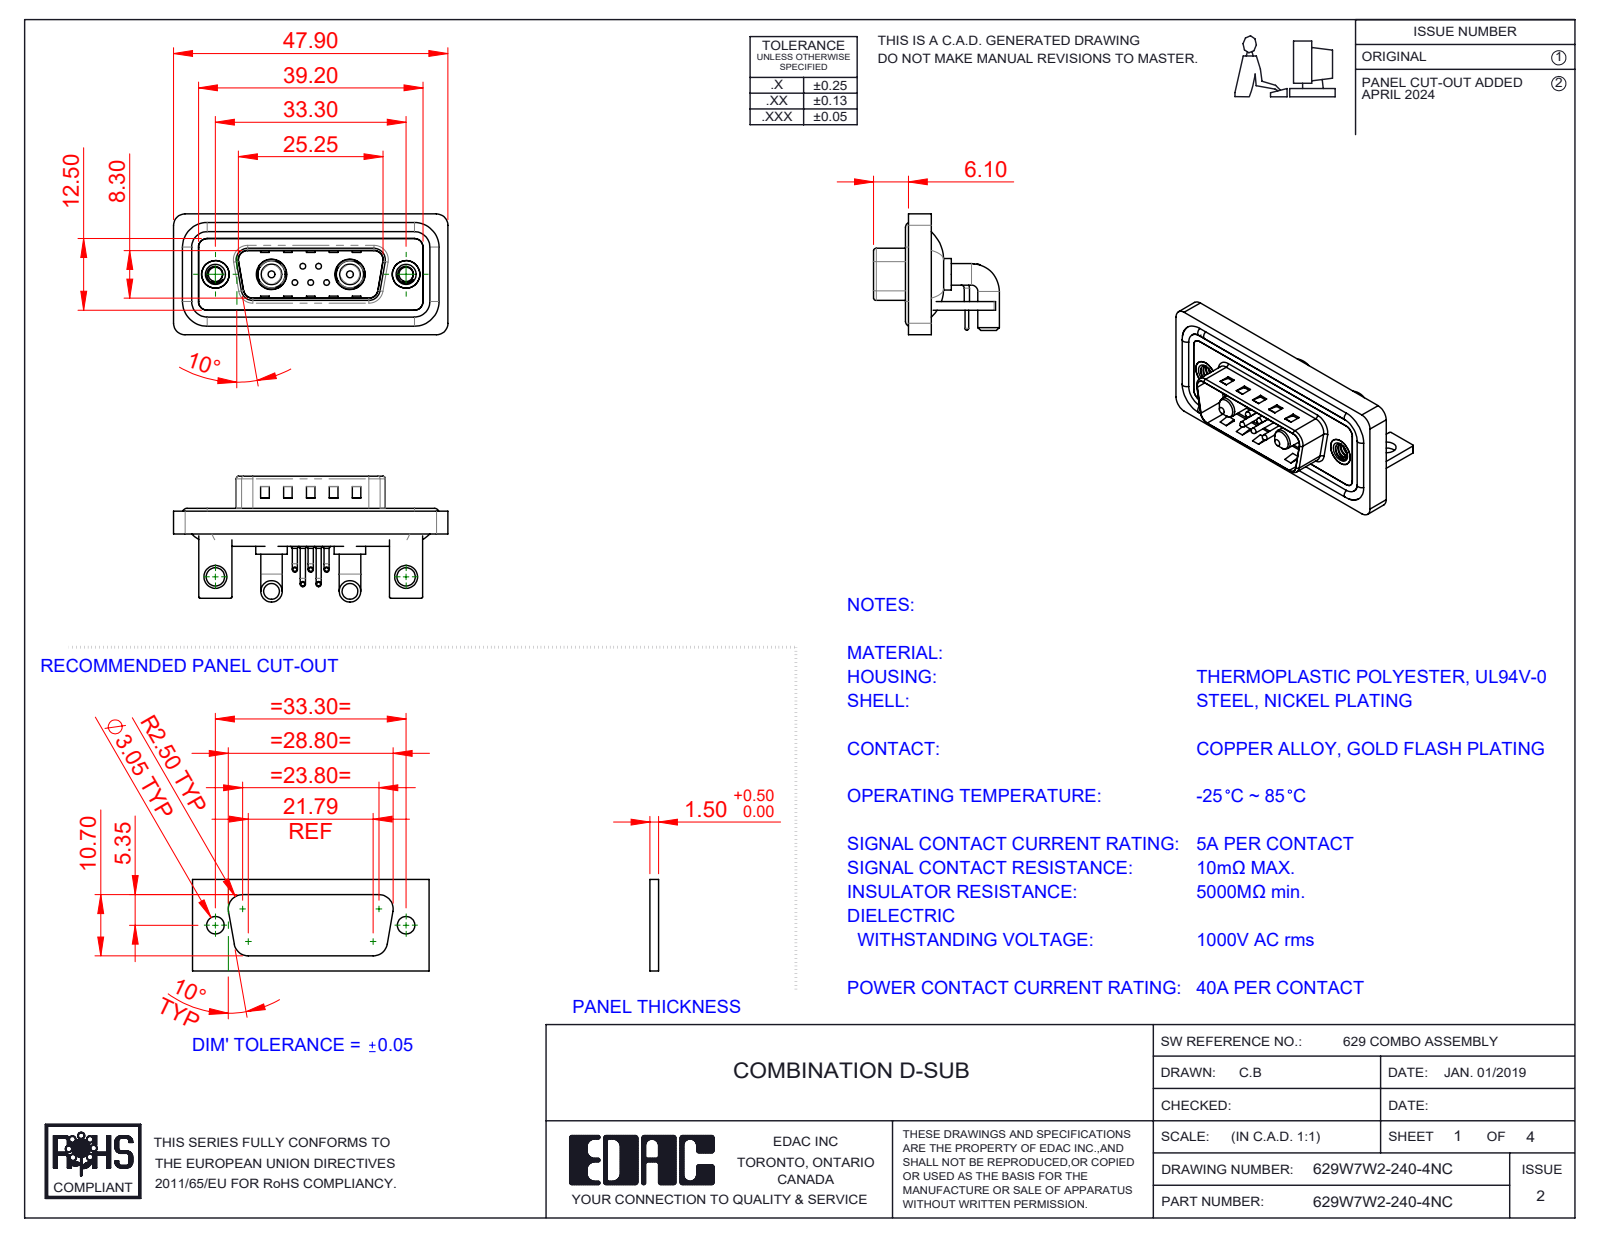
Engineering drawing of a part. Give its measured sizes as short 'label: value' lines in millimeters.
name: 629Combo Contact Row 2; 629Combo Housing_7W2; 629Combo Contact Row 1; 629Combo Shell Rear_15 Contacts (+6 more)
written by: SolidWorks 2023 (CONFIG_CONTROL_DESIGN)
unit: mm
bodies: 18 solids, 1121 faces (537 planar, 424 cylindrical, 160 other)
size: 47.9 × 21.98 × 21.1
volume: 6 098 mm³; area: 9 817 mm²
holes: 5× ⌀0.75, 5× ⌀1.6, 5× ⌀2, 2× ⌀2.5, 2× ⌀3.2, 2× ⌀4, 2× ⌀4.8, 2× ⌀4.85, 2× ⌀5, 2× ⌀5.3
bosses: 10× ⌀0.9, 5× ⌀1.5, 5× ⌀1, 5× ⌀0.65, 4× ⌀3.75, 4× ⌀1.6, 2× ⌀5.5, 2× ⌀5.2
rounds: 21× R2, 18× R1.5, 16× R0.25, 9× R0.5, 8× R1.6, 5× R1.01, 4× R0.6, 4× R0.65
face distances: 0.4, 1.5, 0.8, 2.9, 2.1, 1.1, 1.6, 1.2, 3.7, 4.5
hole spacings: 3.16, 2.77, 9.8, 23.5, 33.3, 4.31, 4.33, 5.03
